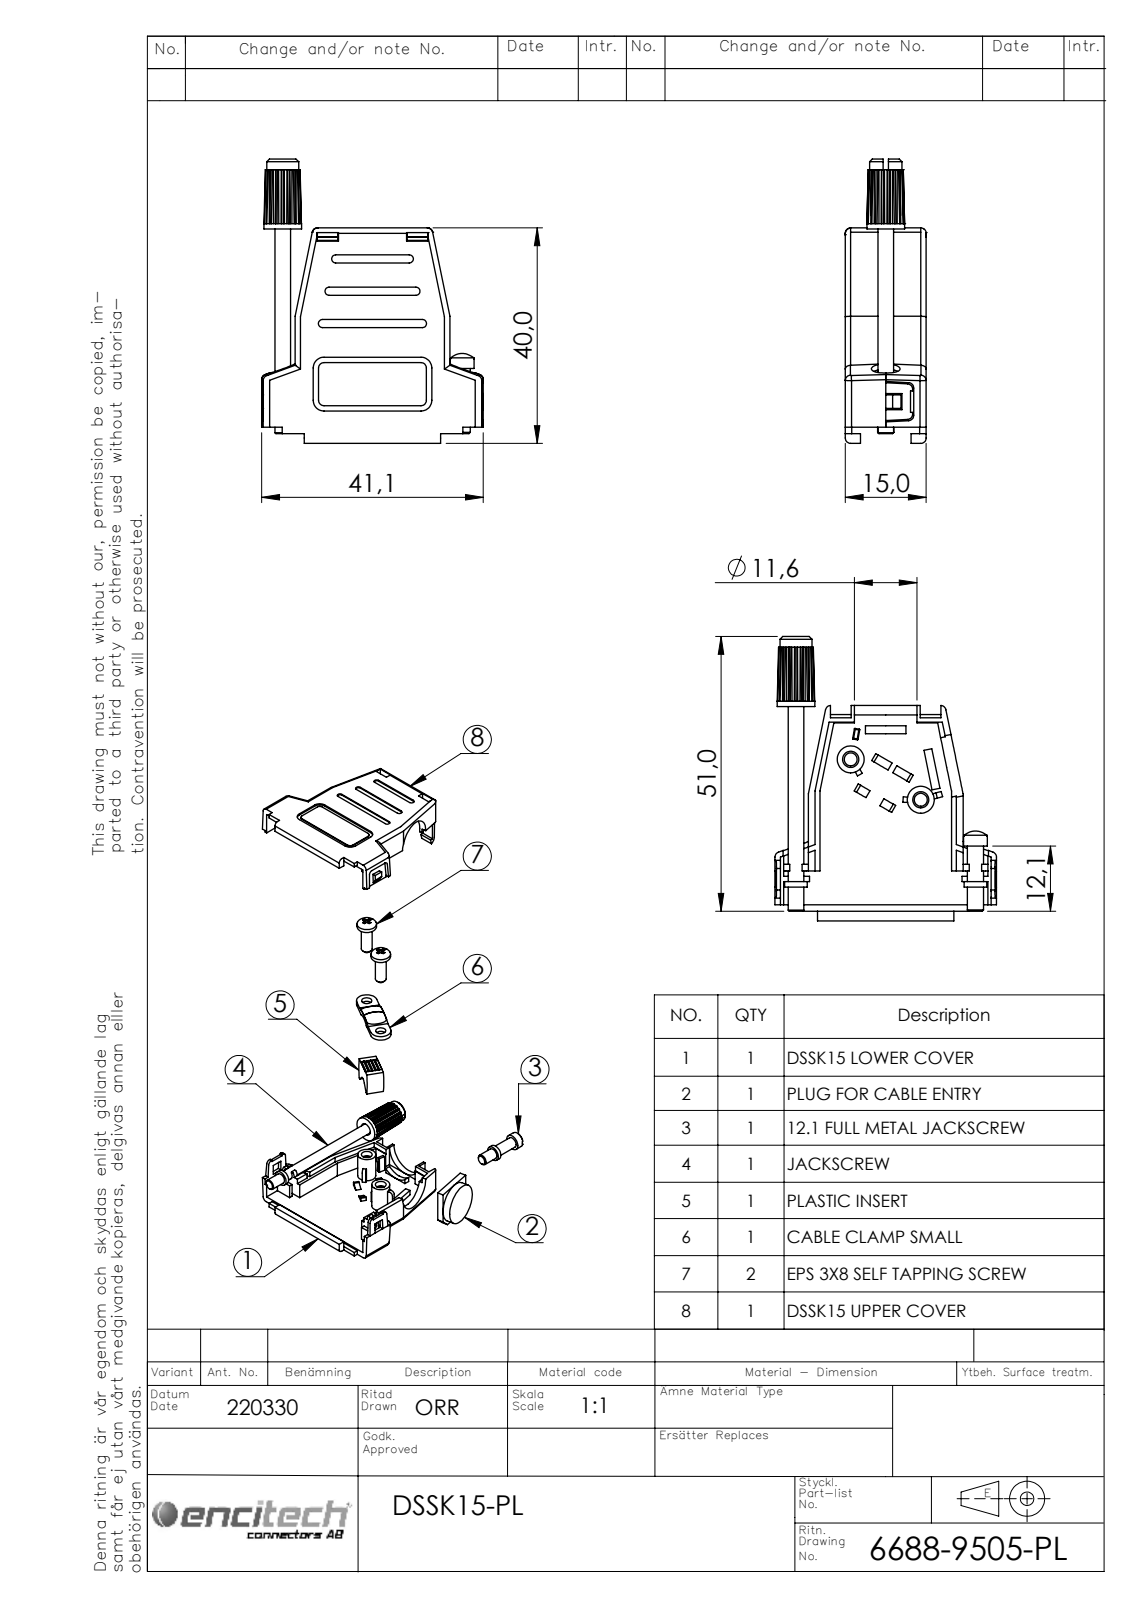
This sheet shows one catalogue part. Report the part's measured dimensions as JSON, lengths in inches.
{"part_name": "6260-0107-02; 6811-0162-11 Part 2; 6826-0133-04; 6718-0101-01 (+5 more)", "step_written_by": "SolidWorks 2021 (AUTOMOTIVE_DESIGN)", "units": "inches", "bodies": {"solids": 11, "faces": 1008, "planar": 683, "cylindrical": 239, "other": 86}, "overall_size": [2.079, 1.618, 0.591], "volume_in3": 0.468, "surface_area_in2": 17.84, "round_holes": [[0.094, 2], [0.11, 2], [0.118, 2], [0.457, 2], [0.03, 1], [0.035, 1], [0.049, 1], [0.098, 1], [0.138, 1], [0.37, 1]], "round_bosses_or_shafts": [[0.215, 2], [0.197, 2], [0.165, 2], [0.449, 1], [0.276, 1], [0.236, 1], [0.173, 1], [0.118, 1]], "partial_cylinders_radius": [[0.039, 31], [0.01, 24], [0.02, 20], [0.005, 16], [0.03, 6], [0.079, 6], [0.016, 4], [0.047, 4]], "face_to_face_distances": [0.067, 0.524, 0.457, 0.591, 0.295, 0.287, 0.228, 0.059, 0.047, 0.583], "hole_center_spacings": [0.344, 0.761, 0.296, 0.296, 0.297, 0.307, 0.323, 0.365]}
